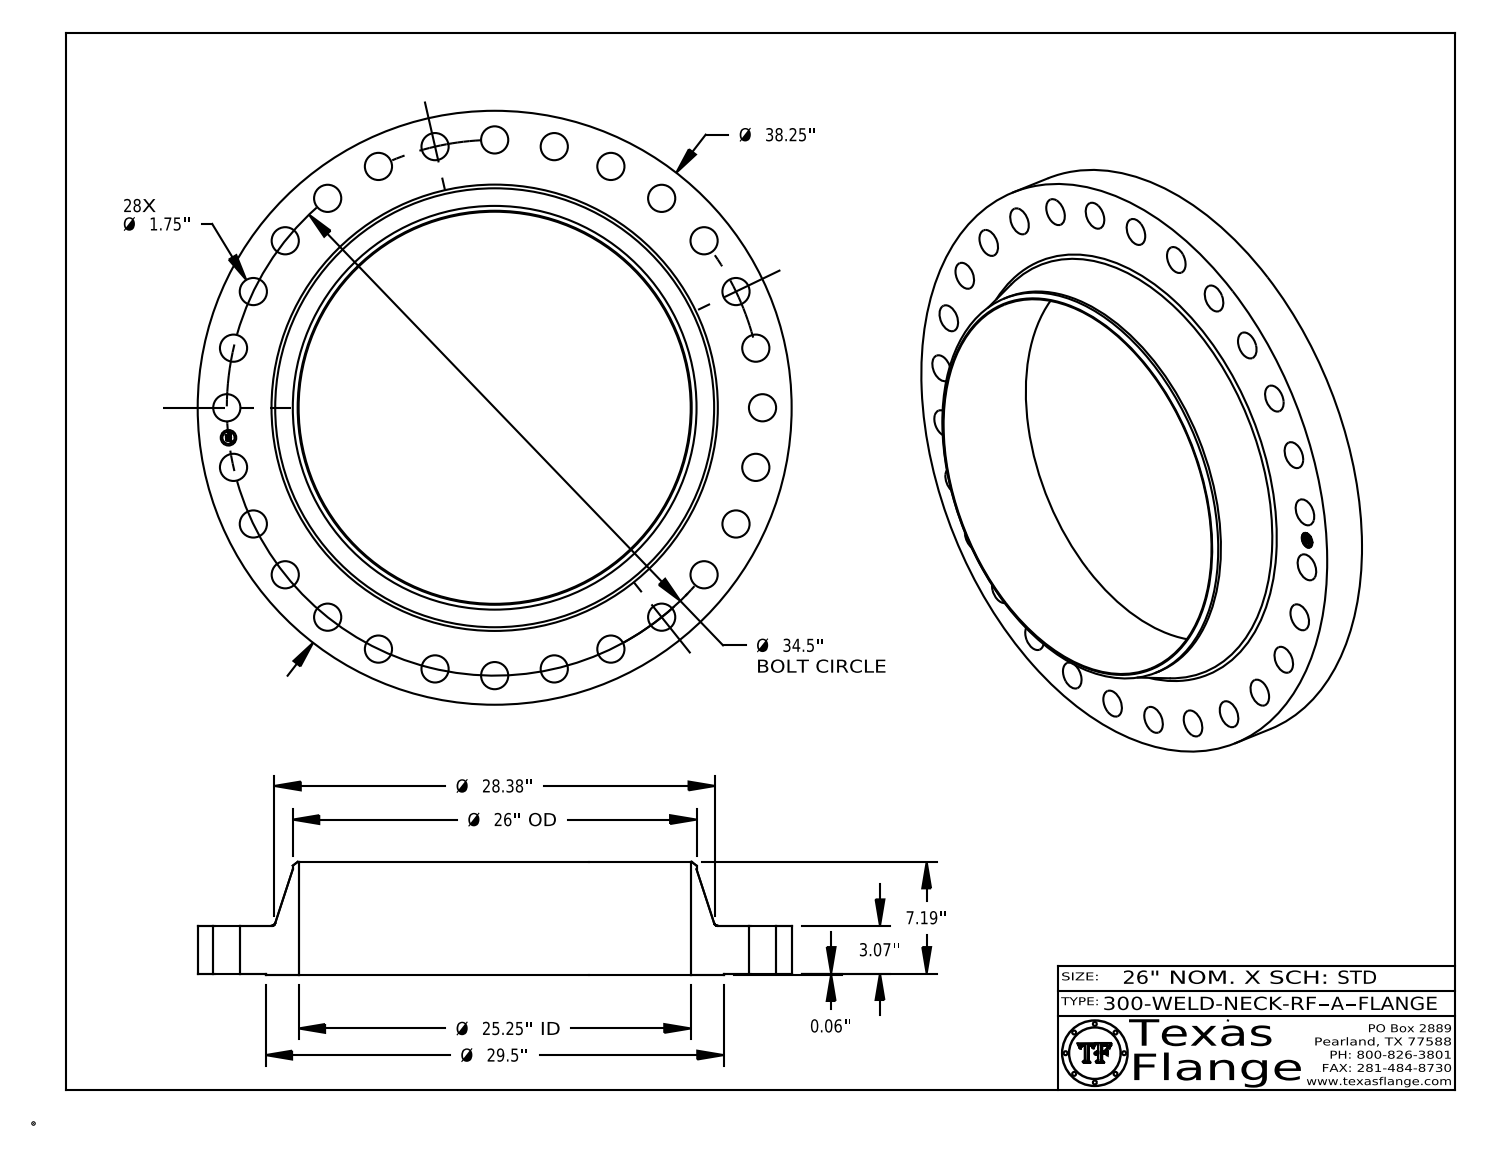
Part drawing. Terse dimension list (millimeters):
name: 300-WELD-NECK-RF, Series A
written by: CATIA V5 STEP AP214 (AUTOMOTIVE_DESIGN)
unit: mm
bodies: 1 solid, 459 faces (369 planar, 84 cylindrical, 6 other)
size: 971.6 × 971.6 × 184.2
volume: 34 410 000 mm³; area: 1 827 000 mm²
holes: 28× ⌀44.5, 1× ⌀25.4, 1× ⌀641.4
bosses: 8× ⌀1.5, 1× ⌀971.6, 1× ⌀749.3, 1× ⌀660.4, 1× ⌀20
face distances: 78, 1.6, 79.6, 184.2, 182.6, 104.6, 0.4, 79.2, 77.6, 105
hole spacings: 438.2, 685.1, 870.8, 380.2, 466.2, 827.1, 854.3, 289.4
